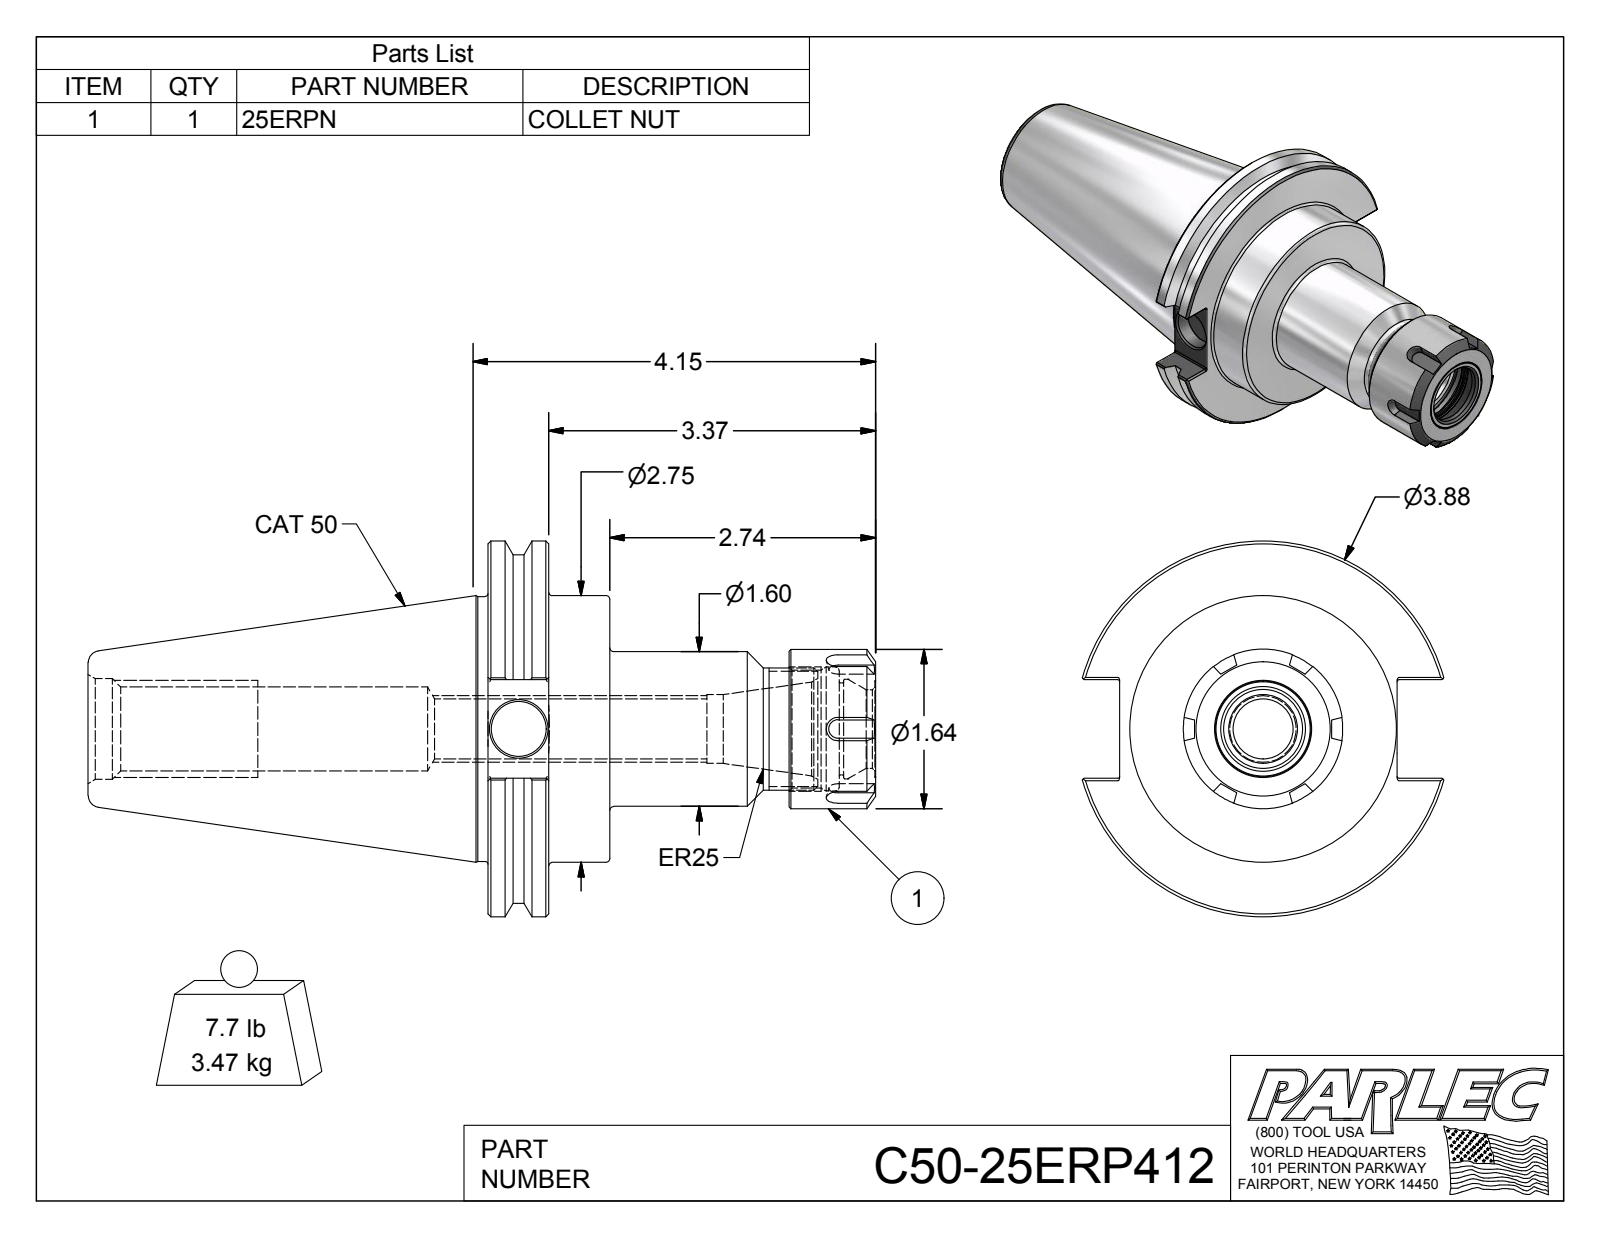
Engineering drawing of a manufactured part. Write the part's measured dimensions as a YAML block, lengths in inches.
part_name: "C50-25ERP412; C50-25ER4-1; 25ERPN"
step_written_by: "Autodesk Inventor 2012 (AUTOMOTIVE_DESIGN)"
units: inches
bodies: {solids: 2, faces: 125, planar: 52, cylindrical: 30, other: 43}
overall_size: [8.12, 3.875, 3.729]
volume: 27.15
surface_area: 98.59
round_holes:
  - {diameter: 0.315, count: 1}
  - {diameter: 0.399, count: 1}
  - {diameter: 0.62, count: 1}
  - {diameter: 0.71, count: 1}
  - {diameter: 0.811, count: 1}
  - {diameter: 0.865, count: 1}
  - {diameter: 0.95, count: 1}
  - {diameter: 1.027, count: 1}
  - {diameter: 1.038, count: 1}
  - {diameter: 1.217, count: 1}
  - {diameter: 1.28, count: 1}
round_bosses_or_shafts:
  - {diameter: 3.875, count: 1}
  - {diameter: 3.594, count: 1}
  - {diameter: 2.75, count: 1}
  - {diameter: 2.73, count: 1}
  - {diameter: 1.643, count: 1}
  - {diameter: 1.595, count: 1}
  - {diameter: 1.26, count: 1}
partial_cylinders:
  - {radius: 0.02, count: 8}
face_to_face_distances: [0.625, 1.255, 0.63, 3.995, 3.37, 2.74, 3.102, 2.477, 1.847, 0.893]
